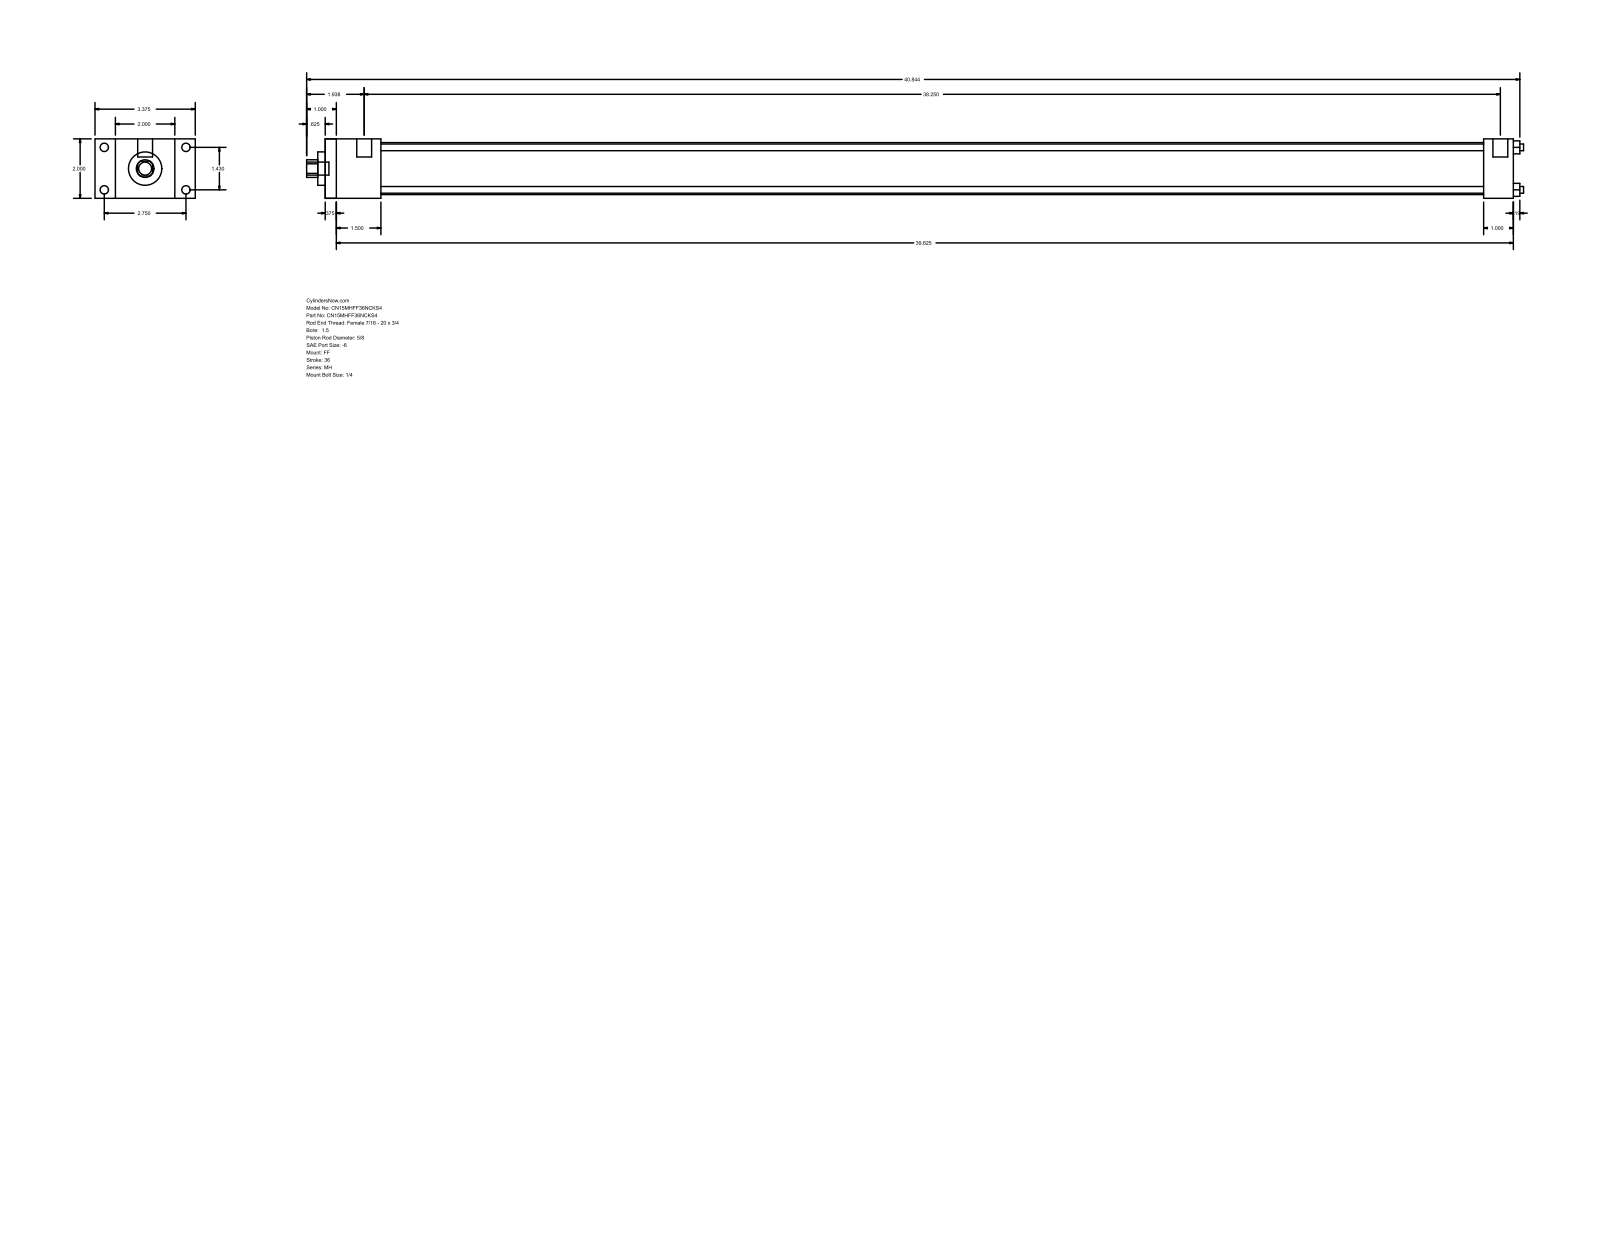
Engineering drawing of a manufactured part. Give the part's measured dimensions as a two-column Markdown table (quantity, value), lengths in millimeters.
| quantity | value |
| --- | --- |
| part name | MH_FF__0150_0.625 |
| STEP written by | GSSL Pune (CONFIG_CONTROL_DESIGN) |
| units | millimeters |
| bodies | 0 solids, 92 faces (64 planar, 28 cylindrical, 0 other) |
| overall size | 1040.61 × 85.72 × 50.8 |
| round holes (diameter × count) | 5.71 × 4, 15.88 × 1, 28.57 × 1, 44.45 × 1 |
| round bosses / shafts (diameter × count) | 7.14 × 4, 5.56 × 4, 12.7 × 2, 11.11 × 1 |
| partial cylindrical surfaces (radius × count) | 7.54 × 1 |
| main face-to-face distances | 50.8, 1016, 9.52, 1006.48, 25.4, 17.46, 68.26, 47.62, 38.1, 968.38 |
| hole center spacings | 25.68, 36.32, 51.36 |
